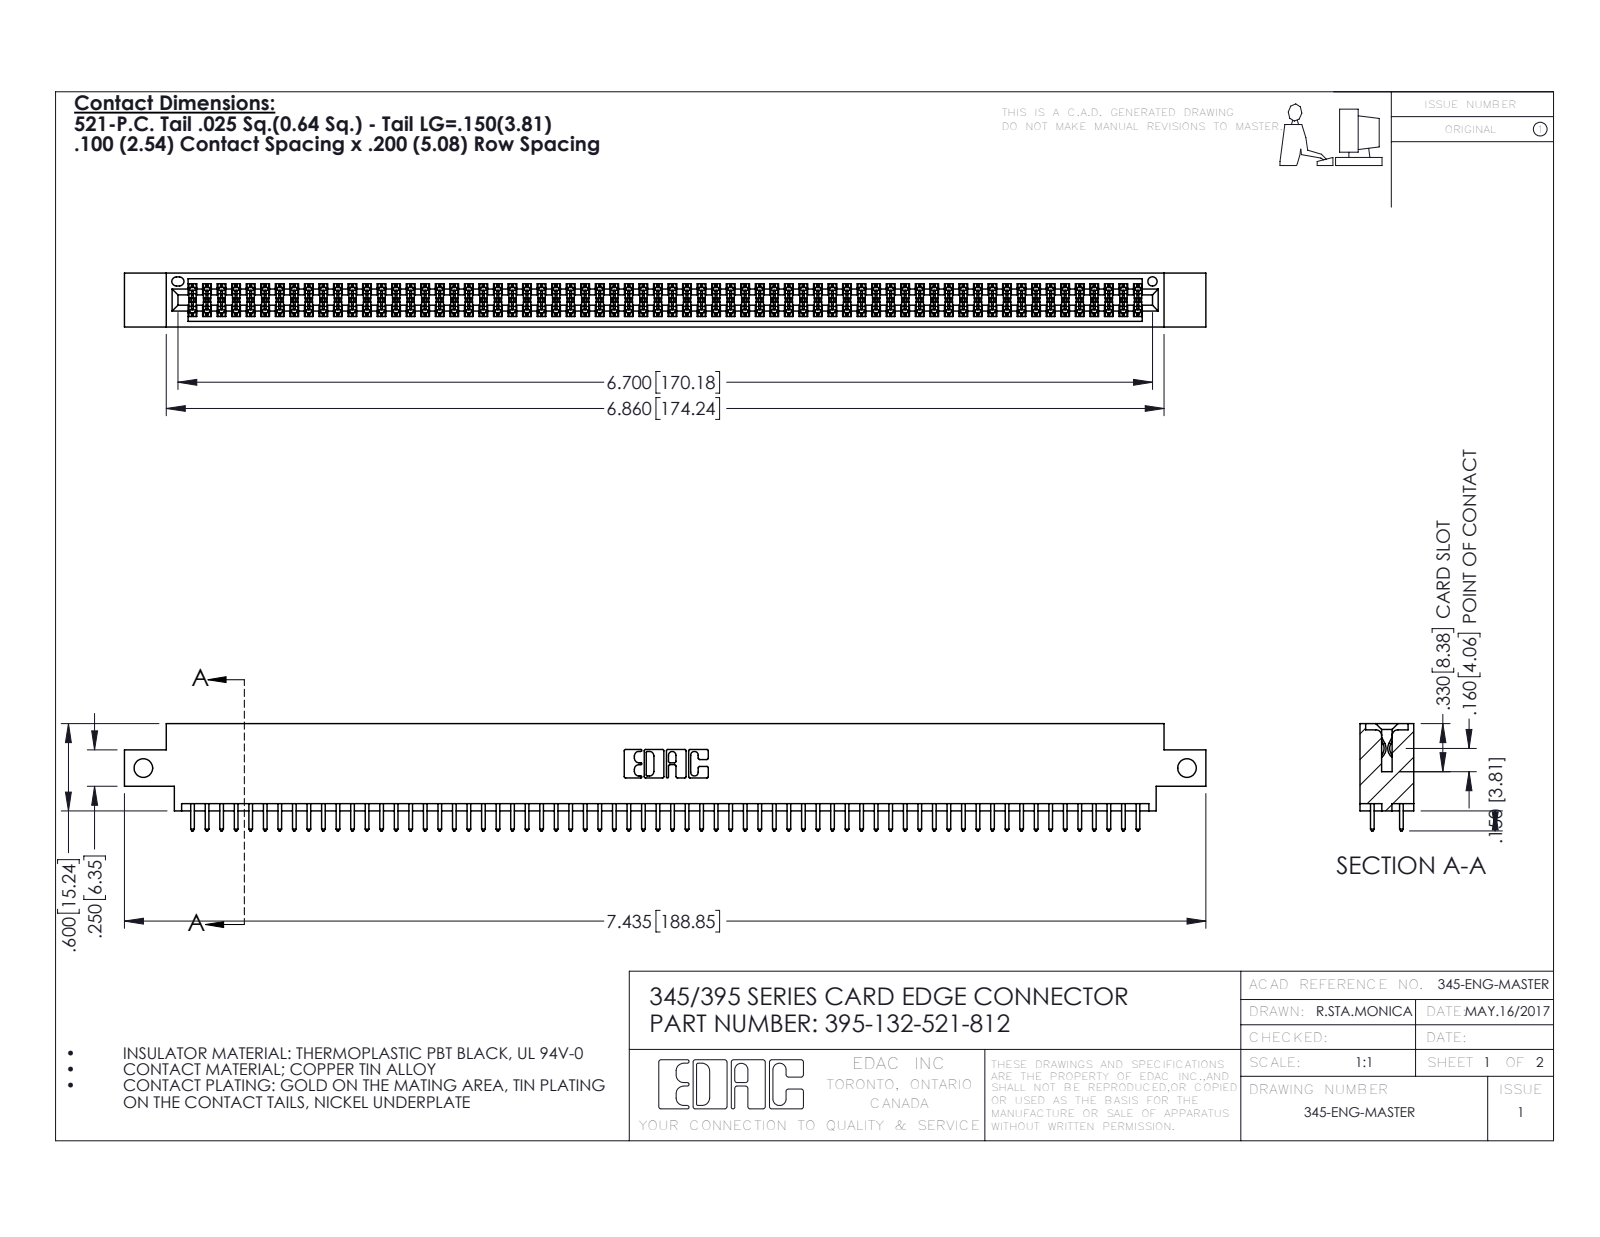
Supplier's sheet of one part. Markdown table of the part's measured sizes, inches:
| quantity | value |
| --- | --- |
| part name | 345 Part_0.170 Offset - Side Mount; 345-292-001_345-293-121; 395-132-521-812 |
| STEP written by | SolidWorks 2016 (CONFIG_CONTROL_DESIGN) |
| units | inches |
| bodies | 133 solids, 6730 faces (4440 planar, 2290 cylindrical, 0 other) |
| overall size | 7.435 × 0.737 × 0.37 |
| volume | 1.118 in³ |
| surface area | 42.15 in² |
| round holes (diameter × count) | 0.128 × 2, 0.064 × 1 |
| partial cylindrical surfaces (radius × count) | 0.006 × 198, 0.01 × 132, 0.01 × 22, 0.007 × 6, 0.031 × 6, 0.026 × 3, 0.014 × 2, 0.019 × 2 |
| main face-to-face distances | 0.298, 0.072, 0.2, 0.37, 0.098, 0.272, 0.025, 0.225, 0.175, 0.149 |
| hole center spacings | 7.175 |
